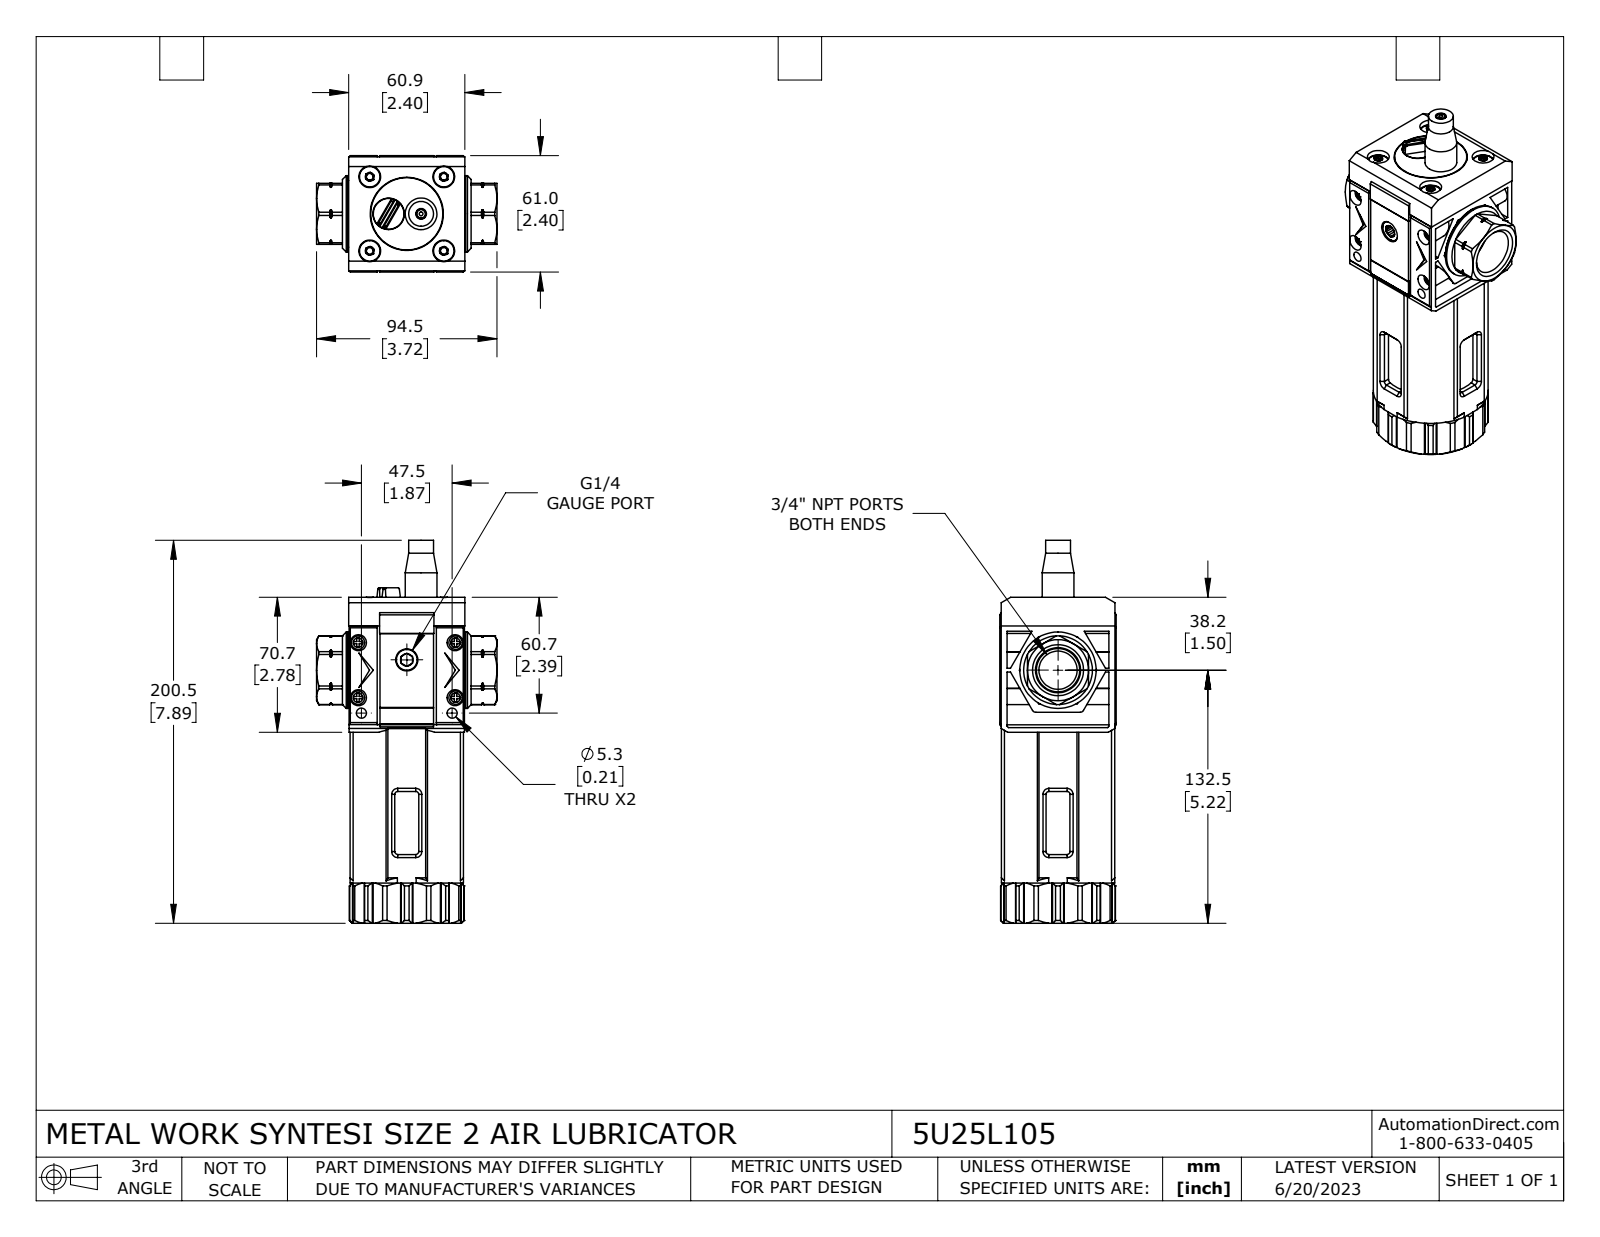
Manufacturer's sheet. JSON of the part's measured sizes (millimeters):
{"part_name": "5U25L105", "step_written_by": "SolidWorks 2021 (CONFIG_CONTROL_DESIGN)", "units": "millimeters", "bodies": {"solids": 14, "faces": 1188, "planar": 543, "cylindrical": 366, "other": 279}, "overall_size": [200.5, 94.5, 61], "volume_mm3": 398700, "surface_area_mm2": 128700, "round_holes": [[3.3, 4], [4.2, 4], [8.4, 4], [11.4, 4], [5.3, 2], [5.6, 1], [11.6, 1], [16.5, 1], [20, 1], [31.8, 1], [38.3, 1], [49, 1]], "round_bosses_or_shafts": [[7, 4], [4.8, 4], [3.8, 4], [40, 1], [37.8, 1], [35, 1], [31.7, 1], [26.3, 1]], "partial_cylinders_radius": [[0.3, 28], [0.5, 16], [1.5, 8], [1.8, 4], [4.9, 4], [0.2, 2], [2, 2], [6.1, 2]], "face_to_face_distances": [60.7, 134.7, 81.4, 53.3, 28.7, 55.7, 15, 45.7, 61, 0.8], "hole_center_spacings": [27.4, 38.8, 8.3, 21.8, 22.8, 26.8, 28.8, 32.1]}
